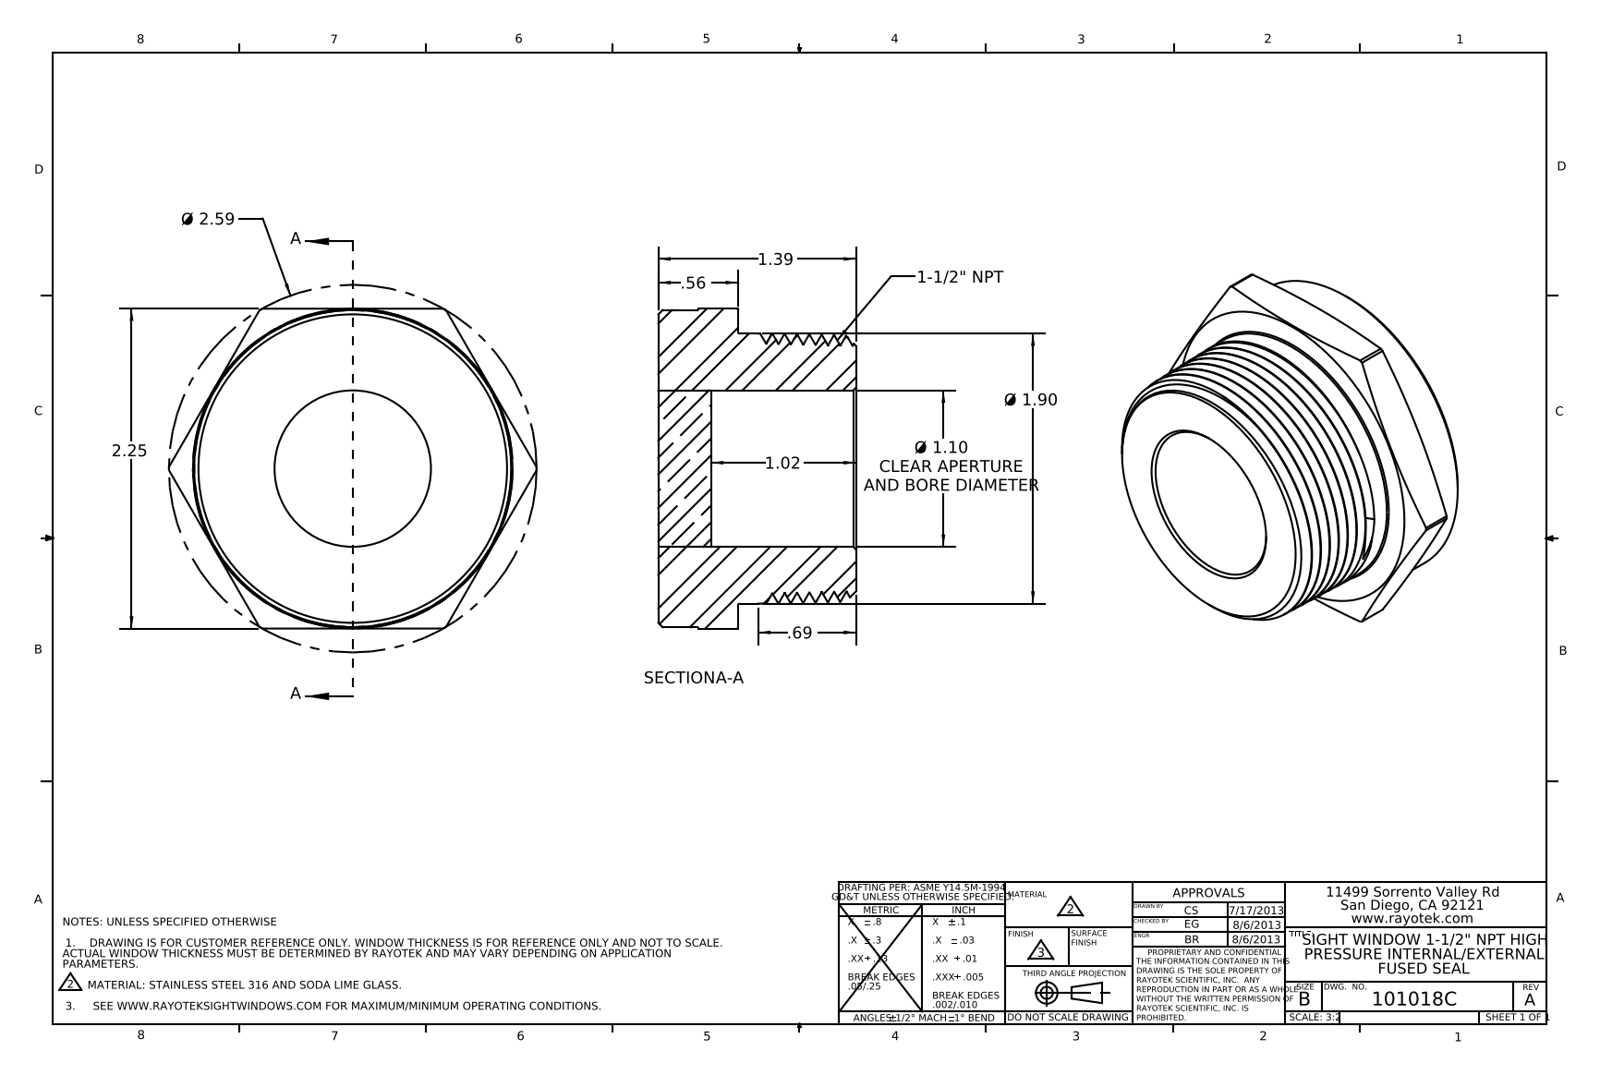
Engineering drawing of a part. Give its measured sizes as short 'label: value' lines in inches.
name: 101018; 402018; 403018_CUSTOMER
written by: SolidWorks 2012 (AUTOMOTIVE_DESIGN)
unit: in
bodies: 2 solids, 62 faces (14 planar, 15 cylindrical, 33 other)
size: 2.586 × 2.25 × 1.39
volume: 3.523 in³; area: 26.14 in²
holes: 1× ⌀1.1
bosses: 1× ⌀2.23, 1× ⌀1.9
rounds: 1× R1.293
face distances: 1.39, 0.56, 0.83, 2.25, 0.37, 0.19, 1.02
